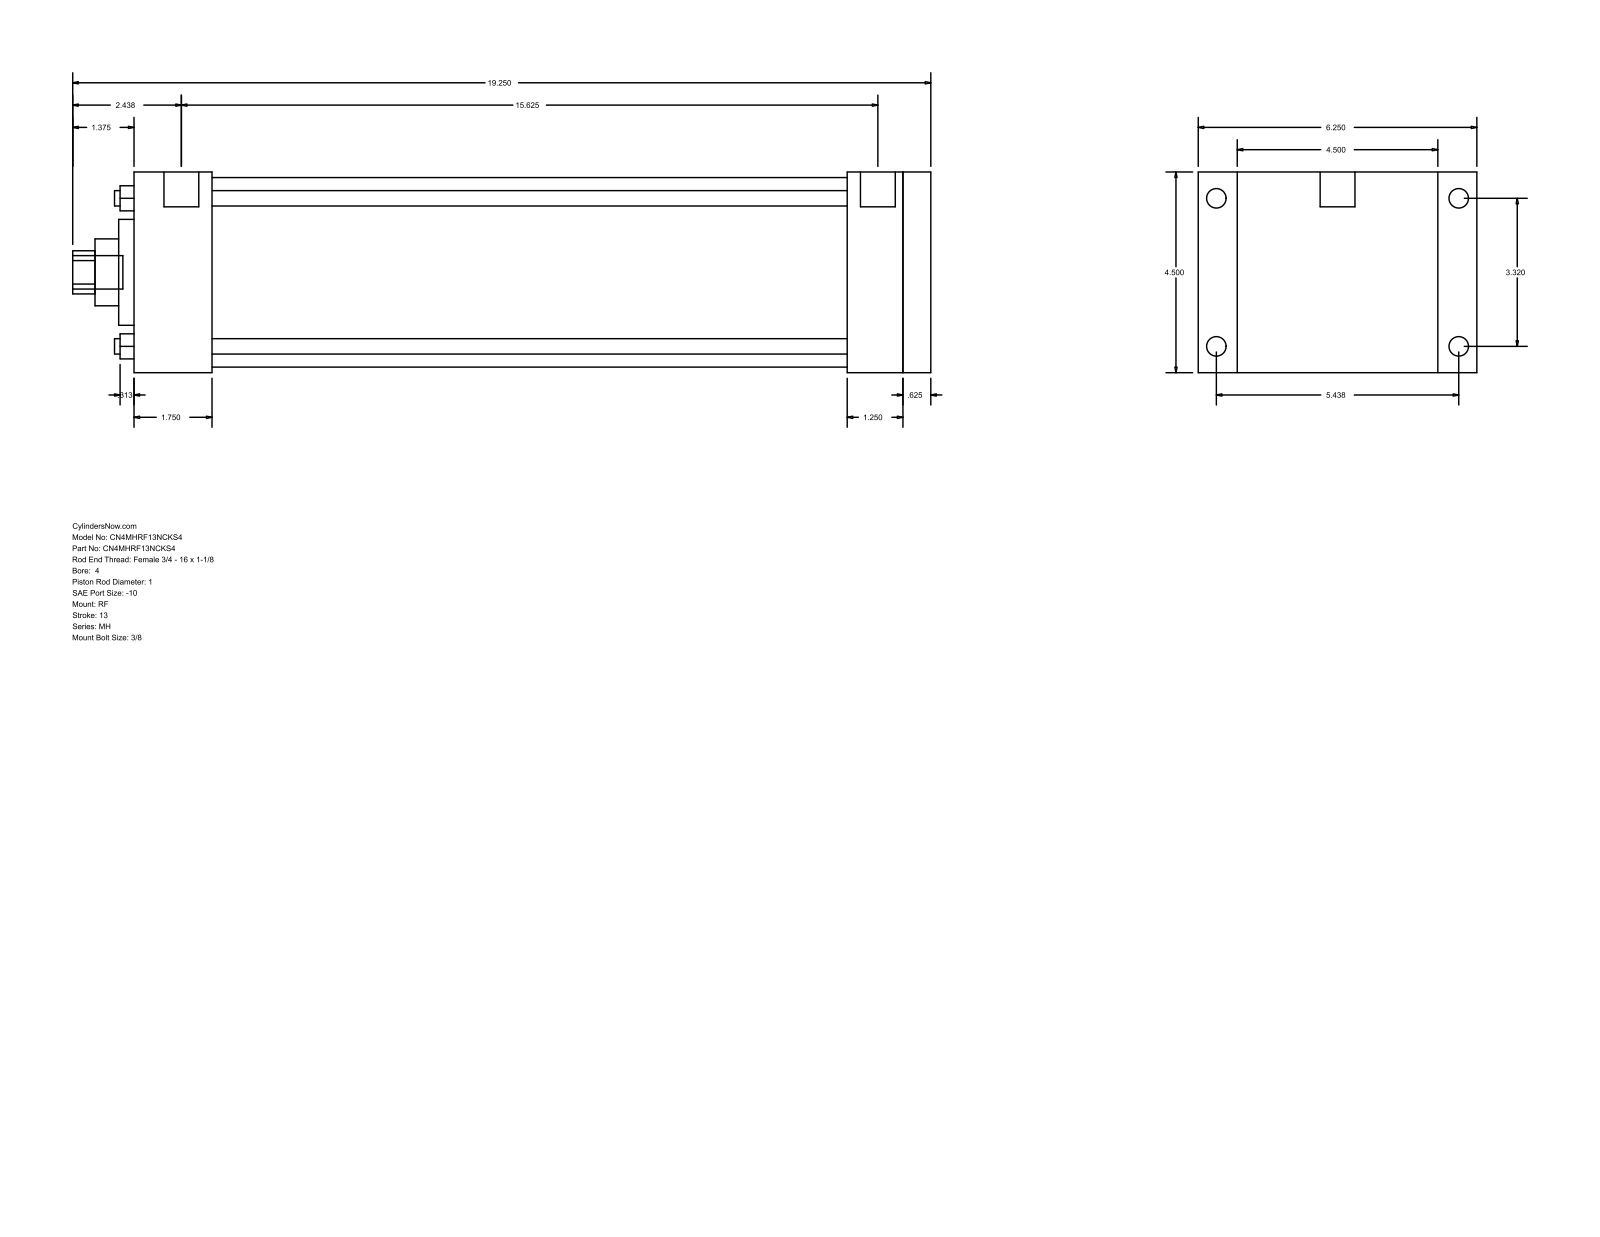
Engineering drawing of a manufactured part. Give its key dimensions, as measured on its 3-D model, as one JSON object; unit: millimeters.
{"part_name": "MH_RF__0400_1", "step_written_by": "GSSL Pune (CONFIG_CONTROL_DESIGN)", "units": "millimeters", "bodies": {"solids": 0, "faces": 94, "planar": 65, "cylindrical": 29, "other": 0}, "overall_size": [488.95, 158.75, 114.3], "round_holes": [[8.76, 4], [25.4, 1], [38.1, 1], [60.33, 1], [107.95, 1]], "round_bosses_or_shafts": [[11.13, 4], [8.73, 4], [19.84, 2], [19.05, 1]], "partial_cylinders_radius": [[12.29, 1]], "face_to_face_distances": [114.3, 454.03, 438.15, 15.88, 47.63, 44.46, 393.69, 409.57, 406.4, 361.94], "hole_center_spacings": [59.62, 84.32, 119.25]}
